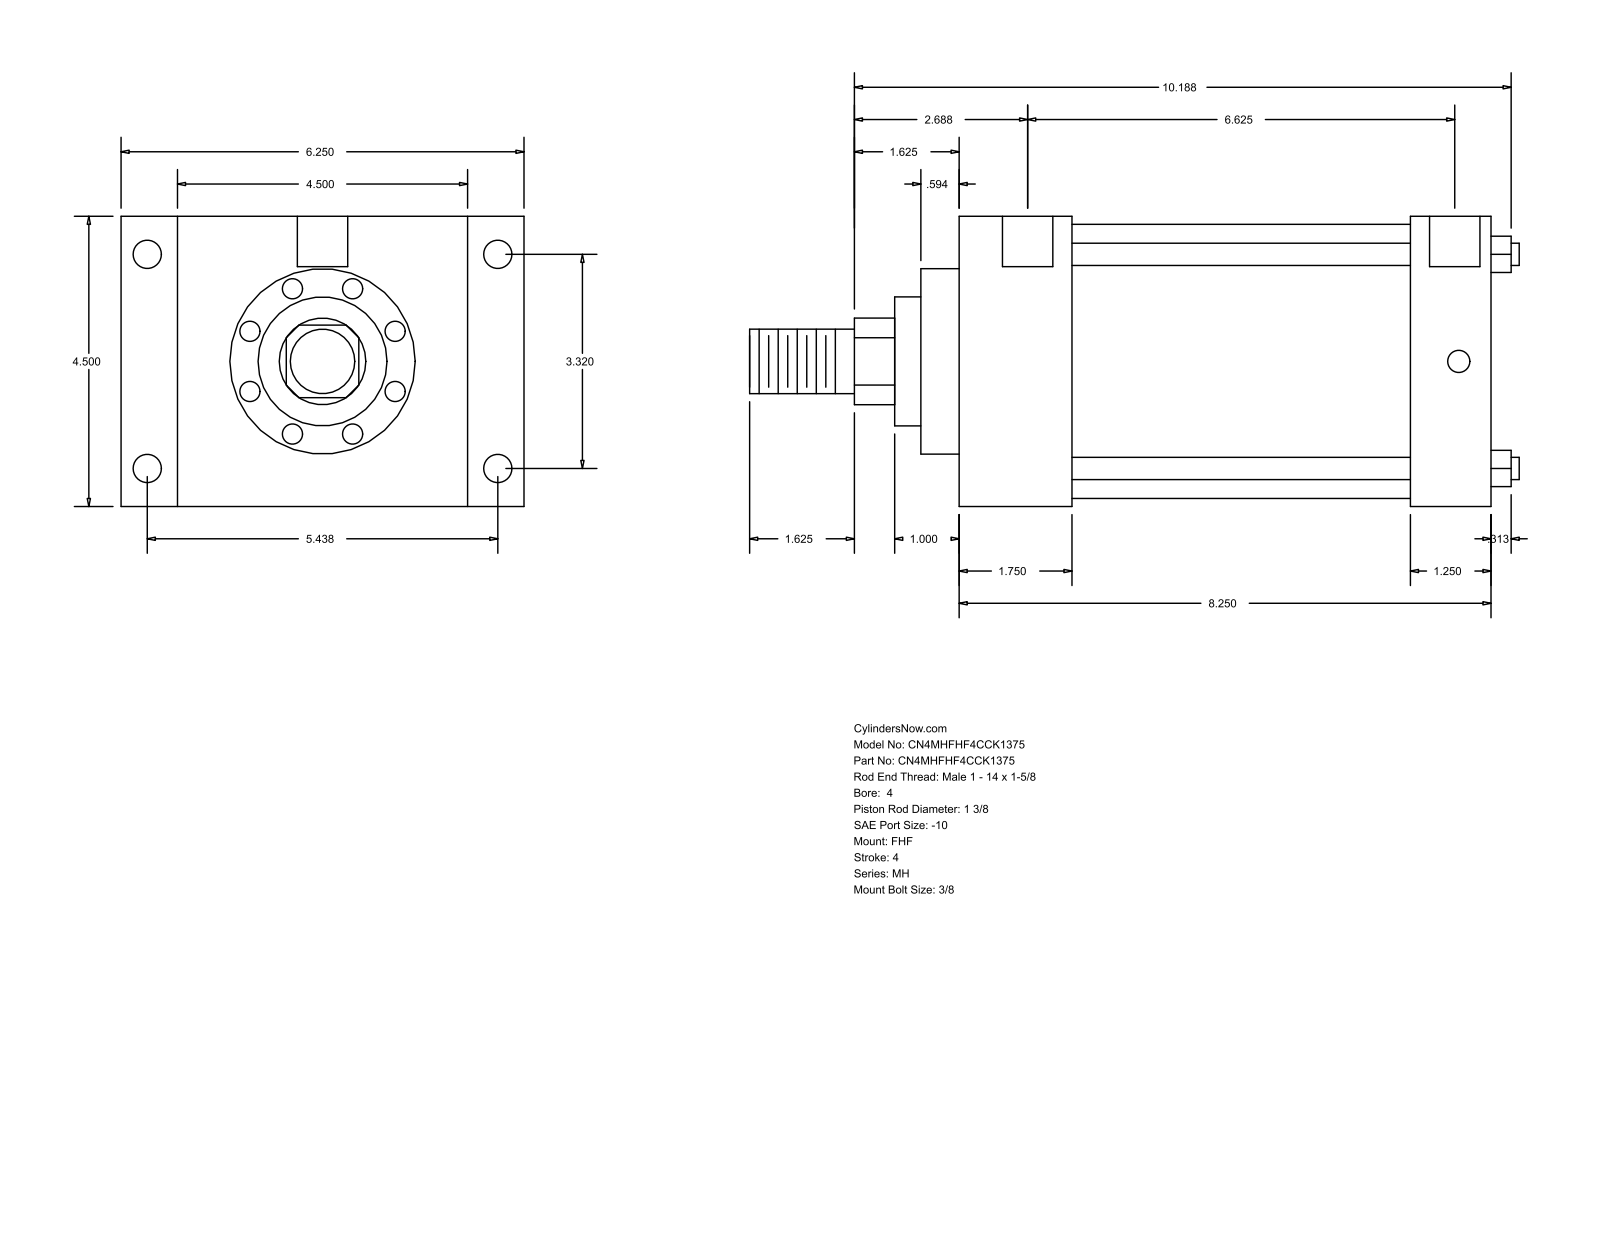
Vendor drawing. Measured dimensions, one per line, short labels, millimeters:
name: MH_FHF__0400_1.375
written by: GSSL Pune (CONFIG_CONTROL_DESIGN)
unit: mm
bodies: 0 solids, 90 faces (61 planar, 29 cylindrical, 0 other)
size: 303.21 × 158.75 × 114.3
holes: 4× ⌀8.73, 4× ⌀11.13, 2× ⌀19.84
bosses: 4× ⌀8.76, 1× ⌀107.95, 1× ⌀73.03, 1× ⌀50.8, 1× ⌀34.92, 1× ⌀25.4
rounds: 1× R17.06
face distances: 114.3, 209.55, 44.45, 165.1, 22.23, 136.53, 158.76, 177.8, 133.35, 31.75
hole spacings: 84.32, 138.12, 161.82, 171.45, 1.58, 1.59, 168.28, 169.86
